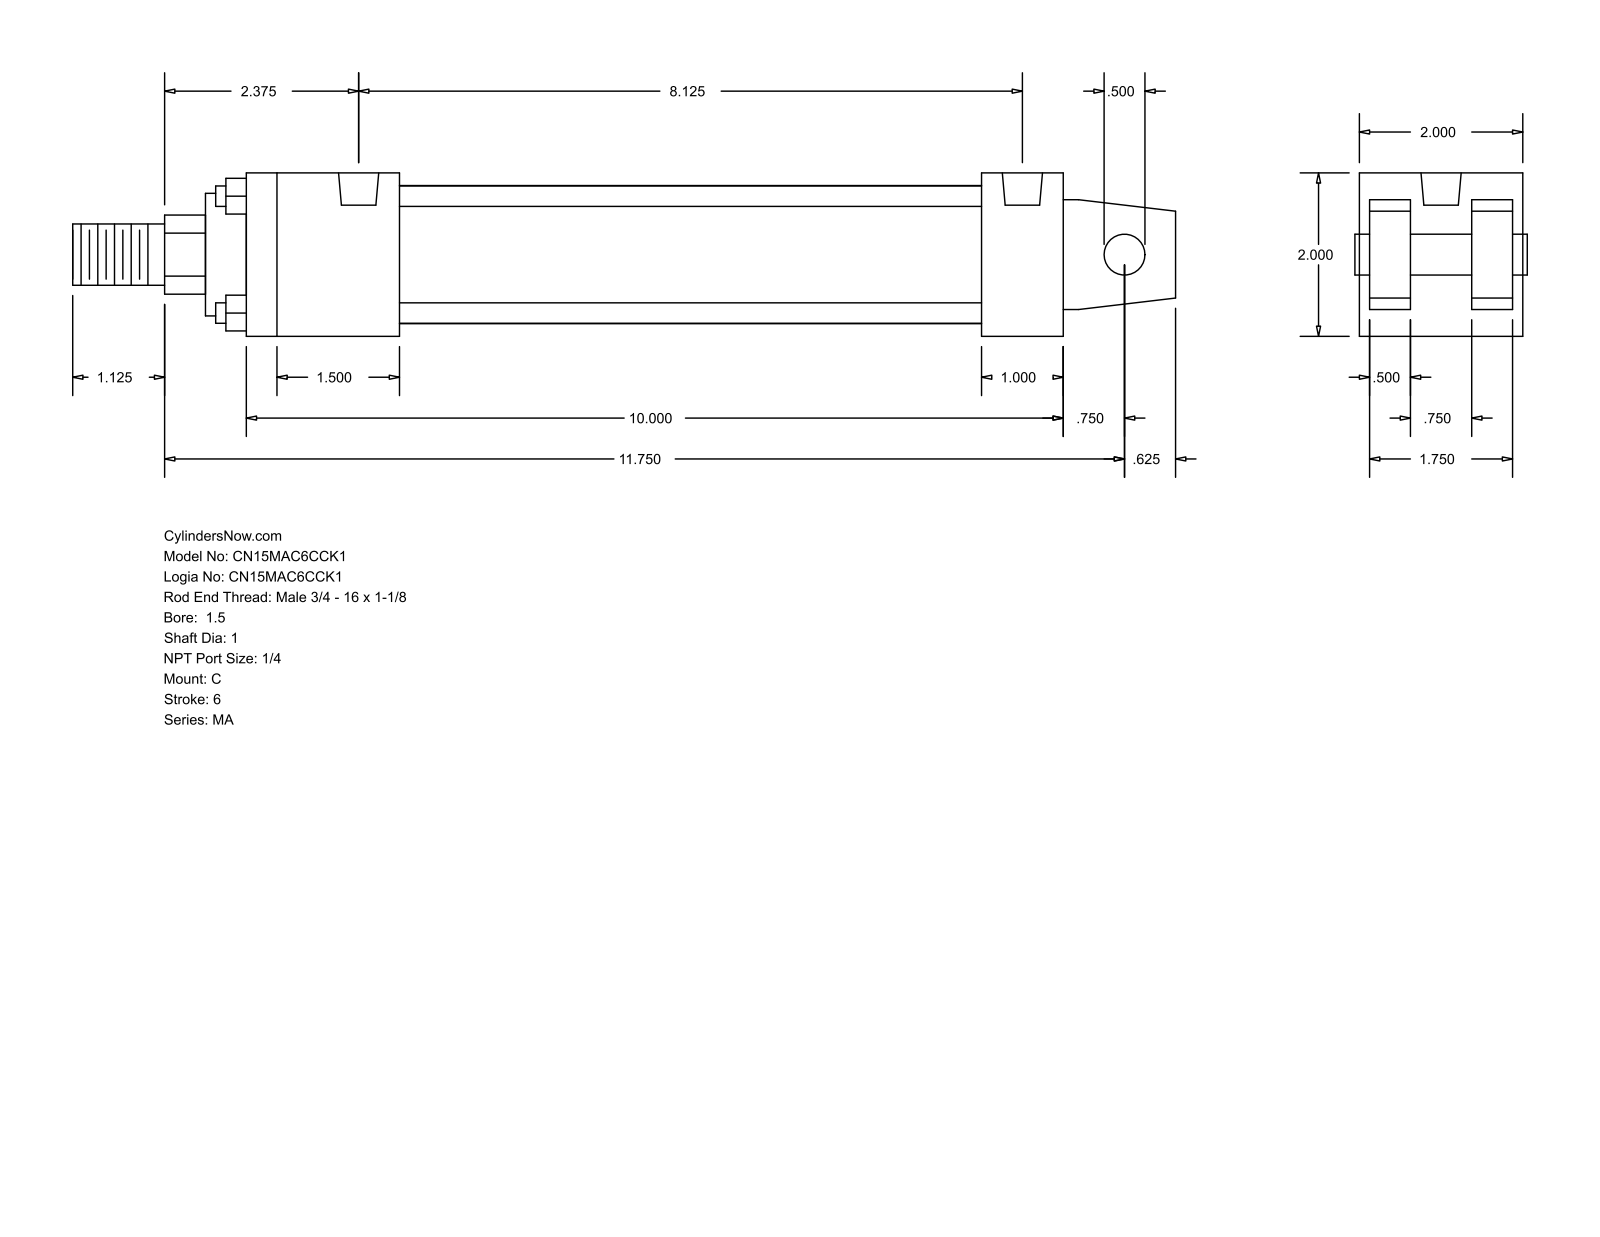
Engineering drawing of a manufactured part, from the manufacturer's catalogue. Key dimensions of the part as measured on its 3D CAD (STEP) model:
Part name (STEP PRODUCT): MA_C__0150_1
STEP written by: GSSL Pune (CONFIG_CONTROL_DESIGN)
Units: millimetres
Bodies: 0 solids, 103 faces (76 planar, 27 cylindrical, 0 other)
Overall size (bounding box): 342.9 × 50.8 × 50.8
Round holes (diameter × count): ⌀7.94 ×4, ⌀12.49 ×2
Round bosses / shafts (diameter × count): ⌀6.35 ×4, ⌀42.93 ×1, ⌀38.1 ×1, ⌀25.4 ×1, ⌀19.05 ×1, ⌀12.7 ×1
Partial cylindrical surfaces — rounded edges, fillets, slot ends (radius × count): R12.29 ×1
Main face-to-face distances: 50.8, 47.63, 12.7, 3.17, 15.87, 34.93, 31.76, 254, 25.4, 228.6
Hole centre spacings: 206.37
